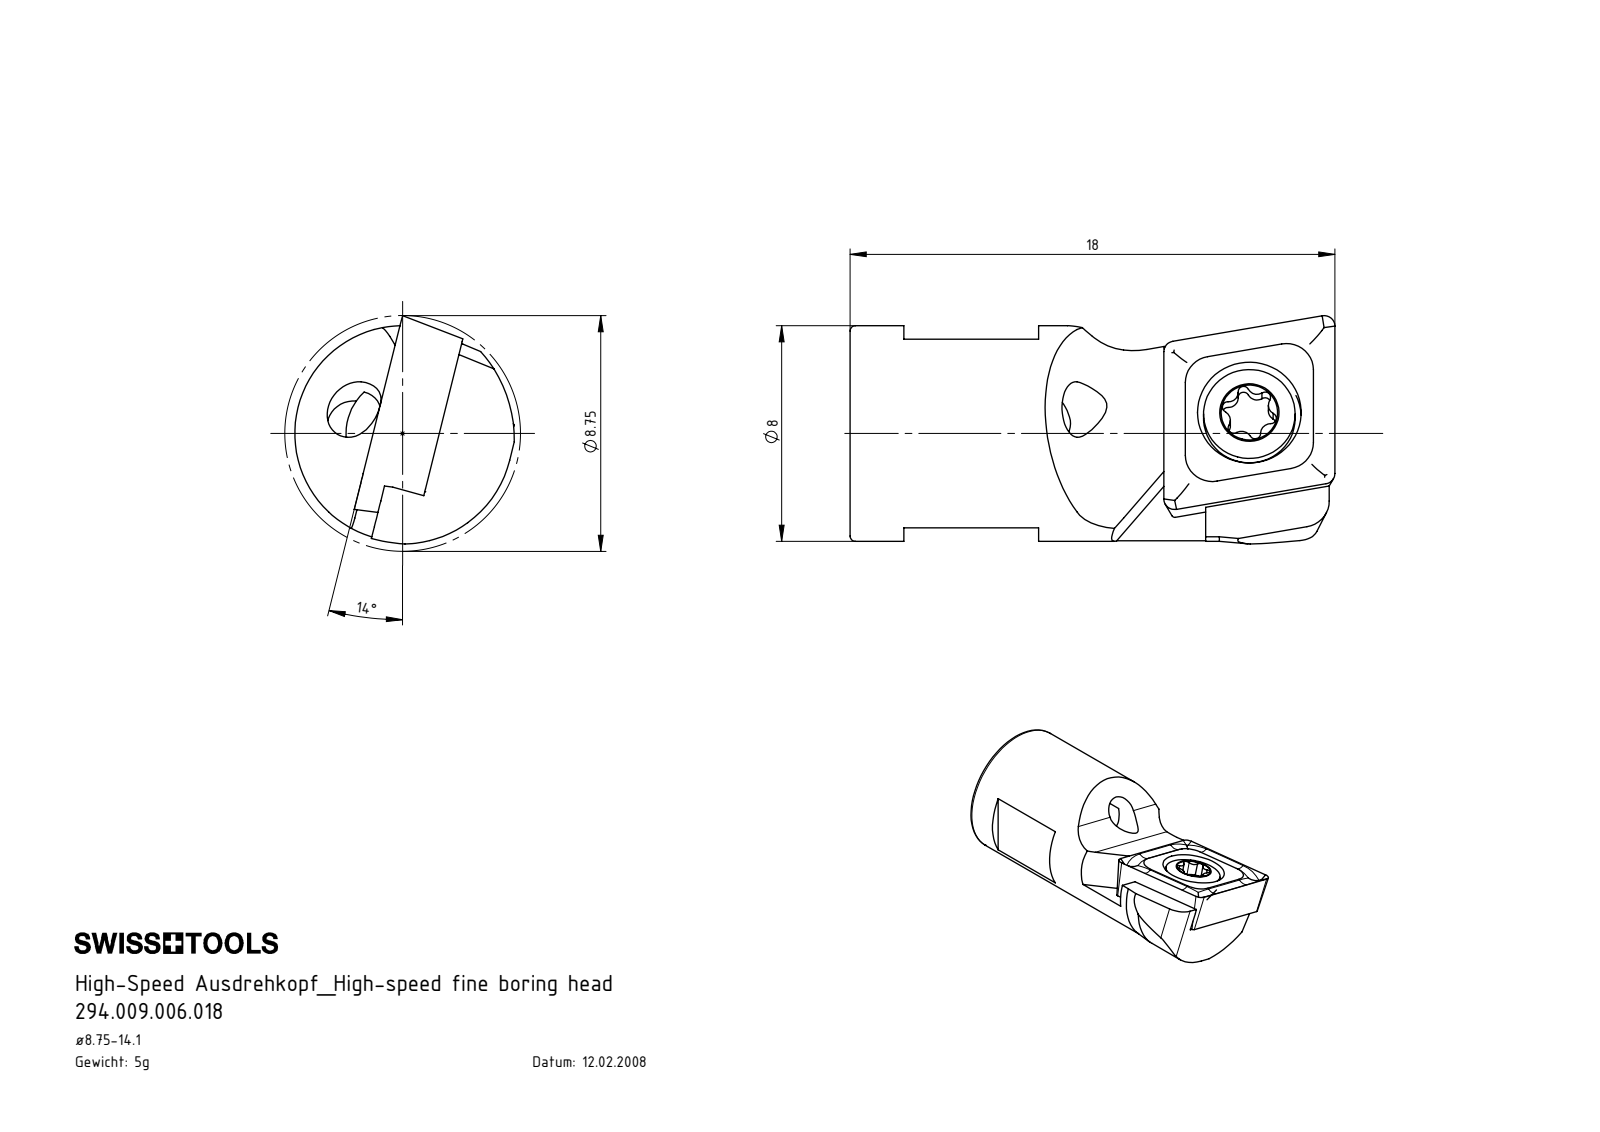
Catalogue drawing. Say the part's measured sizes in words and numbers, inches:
The part is named "HS5.A09.K11.018; CCMT060204; WCA-ER2.001.005_A; HS5-A09.K11.018_D". Its 3-D file was written by "SolidWorks 2017 (AUTOMOTIVE_DESIGN)". It is 3 solids with 129 faces: 40 planar, 38 cylindrical and 51 other. Overall it measures 0.709 by 0.333 by 0.321 inches. Its volume is 0.034 cubic inches and its surface area 1.23 square inches. Round holes: 1 of diameter 0.079, 1 of diameter 0.081, 1 of diameter 0.11, 1 of diameter 0.152, 1 of diameter 0.165. Round bosses or shafts: 1 of diameter 0.315, 1 of diameter 0.134, 1 of diameter 0.098. Partial cylindrical surfaces (rounded edges, fillets, slot ends): 6 of radius 0.008, 5 of radius 0.014, 1 of radius 0.014, 1 of radius 0.039, 1 of radius 0.079, 1 of radius 0.118, 1 of radius 0.161, 1 of radius 0.193. The main face-to-face distances are 0.276, 0.094, 0.09, 0.059, 0.031, 0.035, 0.465, 0.197, 0.189, 0.079.
